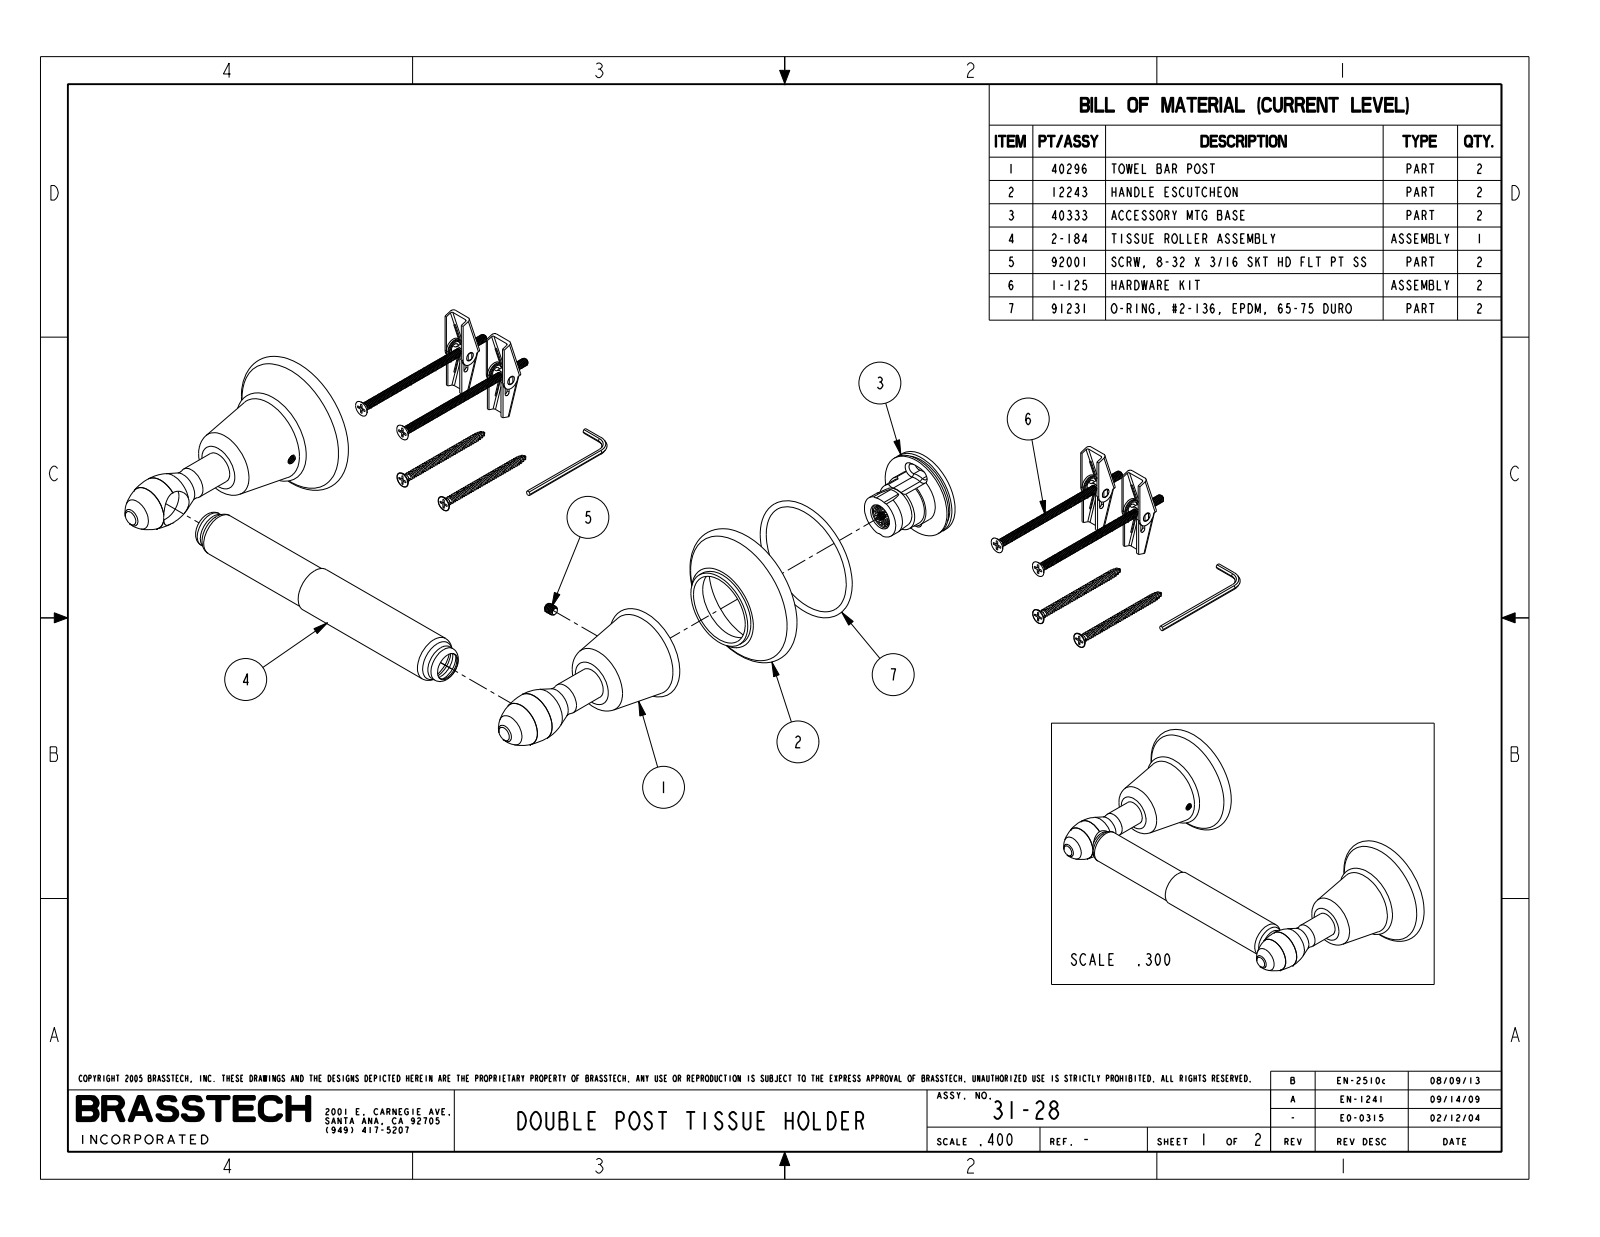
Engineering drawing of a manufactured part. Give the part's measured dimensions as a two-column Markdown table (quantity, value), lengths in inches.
| quantity | value |
| --- | --- |
| part name | 31-28_WEB |
| STEP written by | PRO/ENGINEER BY PARAMETRIC TECHNOLOGY CORPORATION, 2009300 (CONFIG_CONTROL_DESIGN) |
| units | inches |
| bodies | 0 solids, 151 faces (9 planar, 56 cylindrical, 86 other) |
| overall size | 8.6 × 4.153 × 2.35 |
| round holes (diameter × count) | 0.136 × 1 |
| round bosses / shafts (diameter × count) | 0.553 × 2, 0.8 × 1, 0.75 × 1, 0.625 × 1 |
| main face-to-face distances | 1.975, 2.245, 5.09, 2.845, 3.375, 1.4 |
